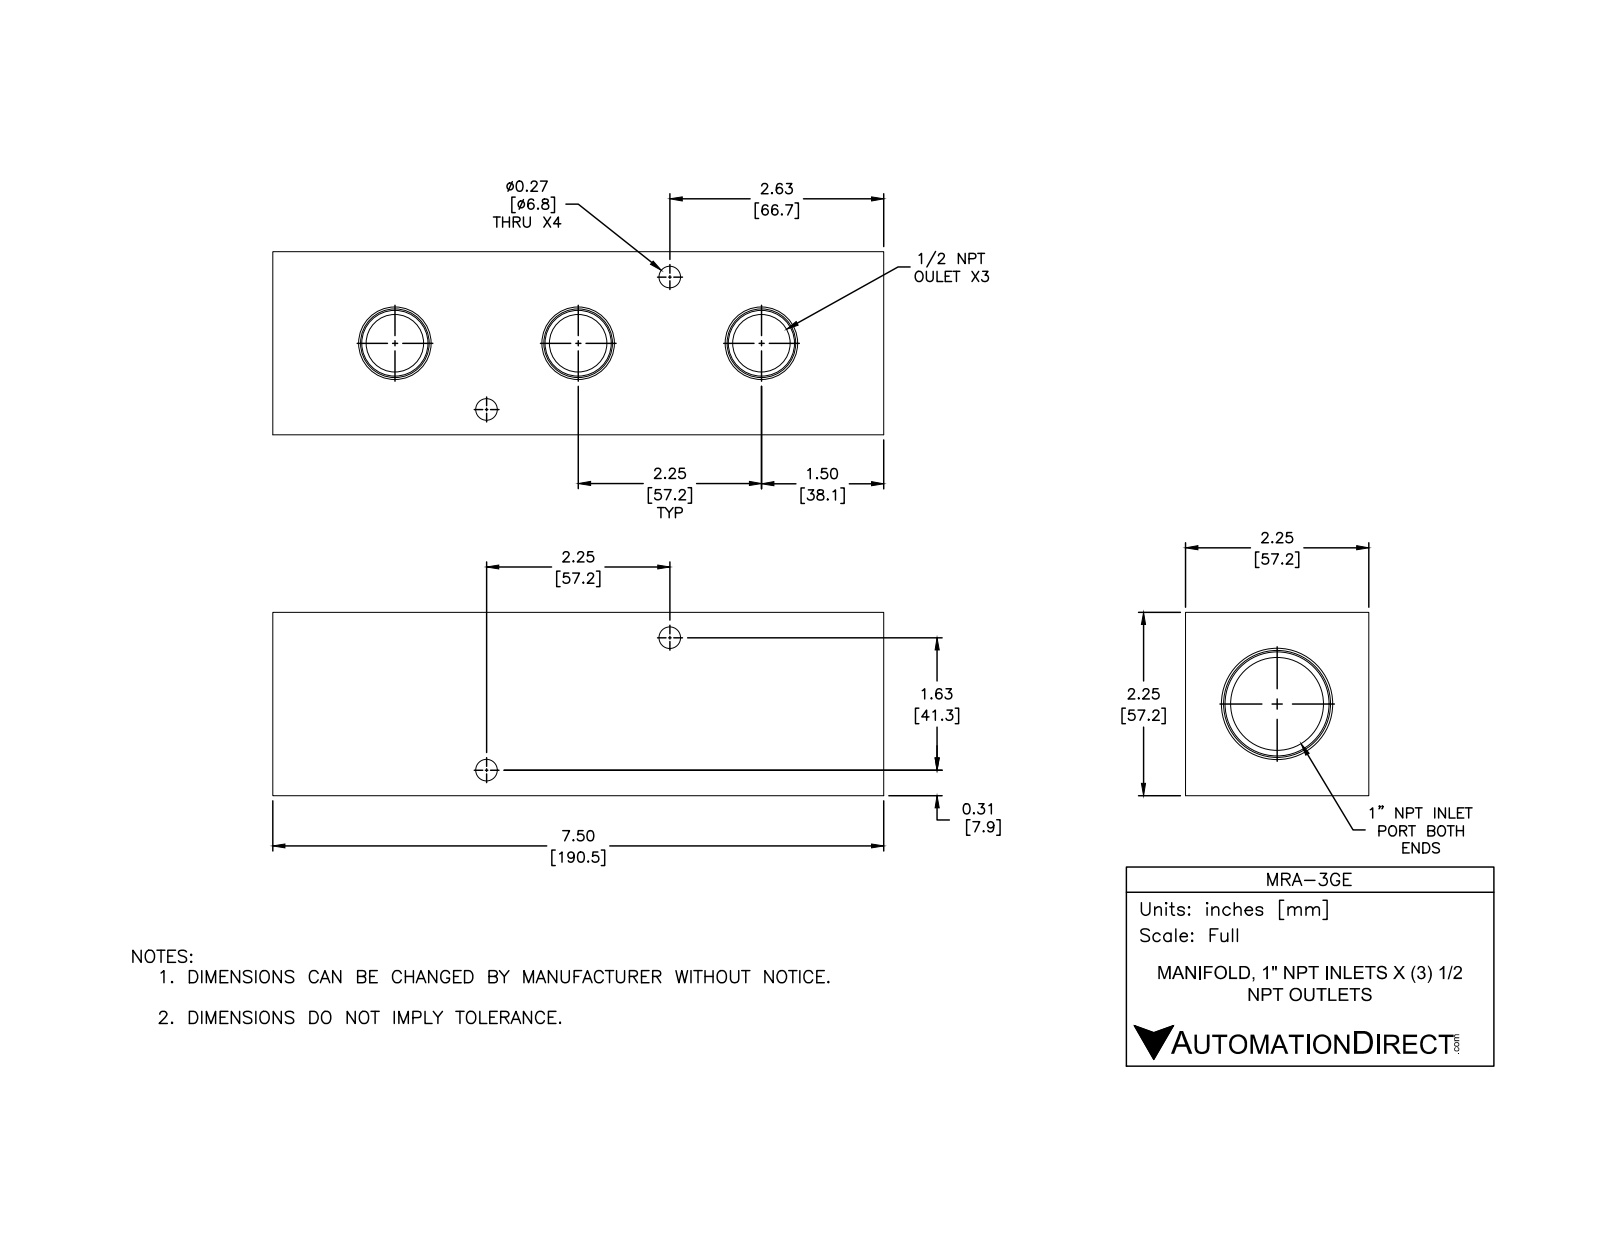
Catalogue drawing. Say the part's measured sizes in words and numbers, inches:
The part is named "MRA-3GE". Its 3-D file was written by "SolidWorks 2015 (CONFIG_CONTROL_DESIGN)". It is 1 solid with 55 faces: 11 planar, 24 cylindrical and 20 other. Overall it measures 7.5 by 2.25 by 2.25 inches. Its volume is 28.51 cubic inches and its surface area 111.4 square inches. Round holes: 4 of diameter 0.266, 3 of diameter 0.703, 1 of diameter 1.141. The main face-to-face distances are 2.25, 7.5, 0.66, 6.84, 1.72, 0.53, 6.18. The hole center spacings are 1.388, 2.25, 2.776, 3.471, 3.472, 4.5.
